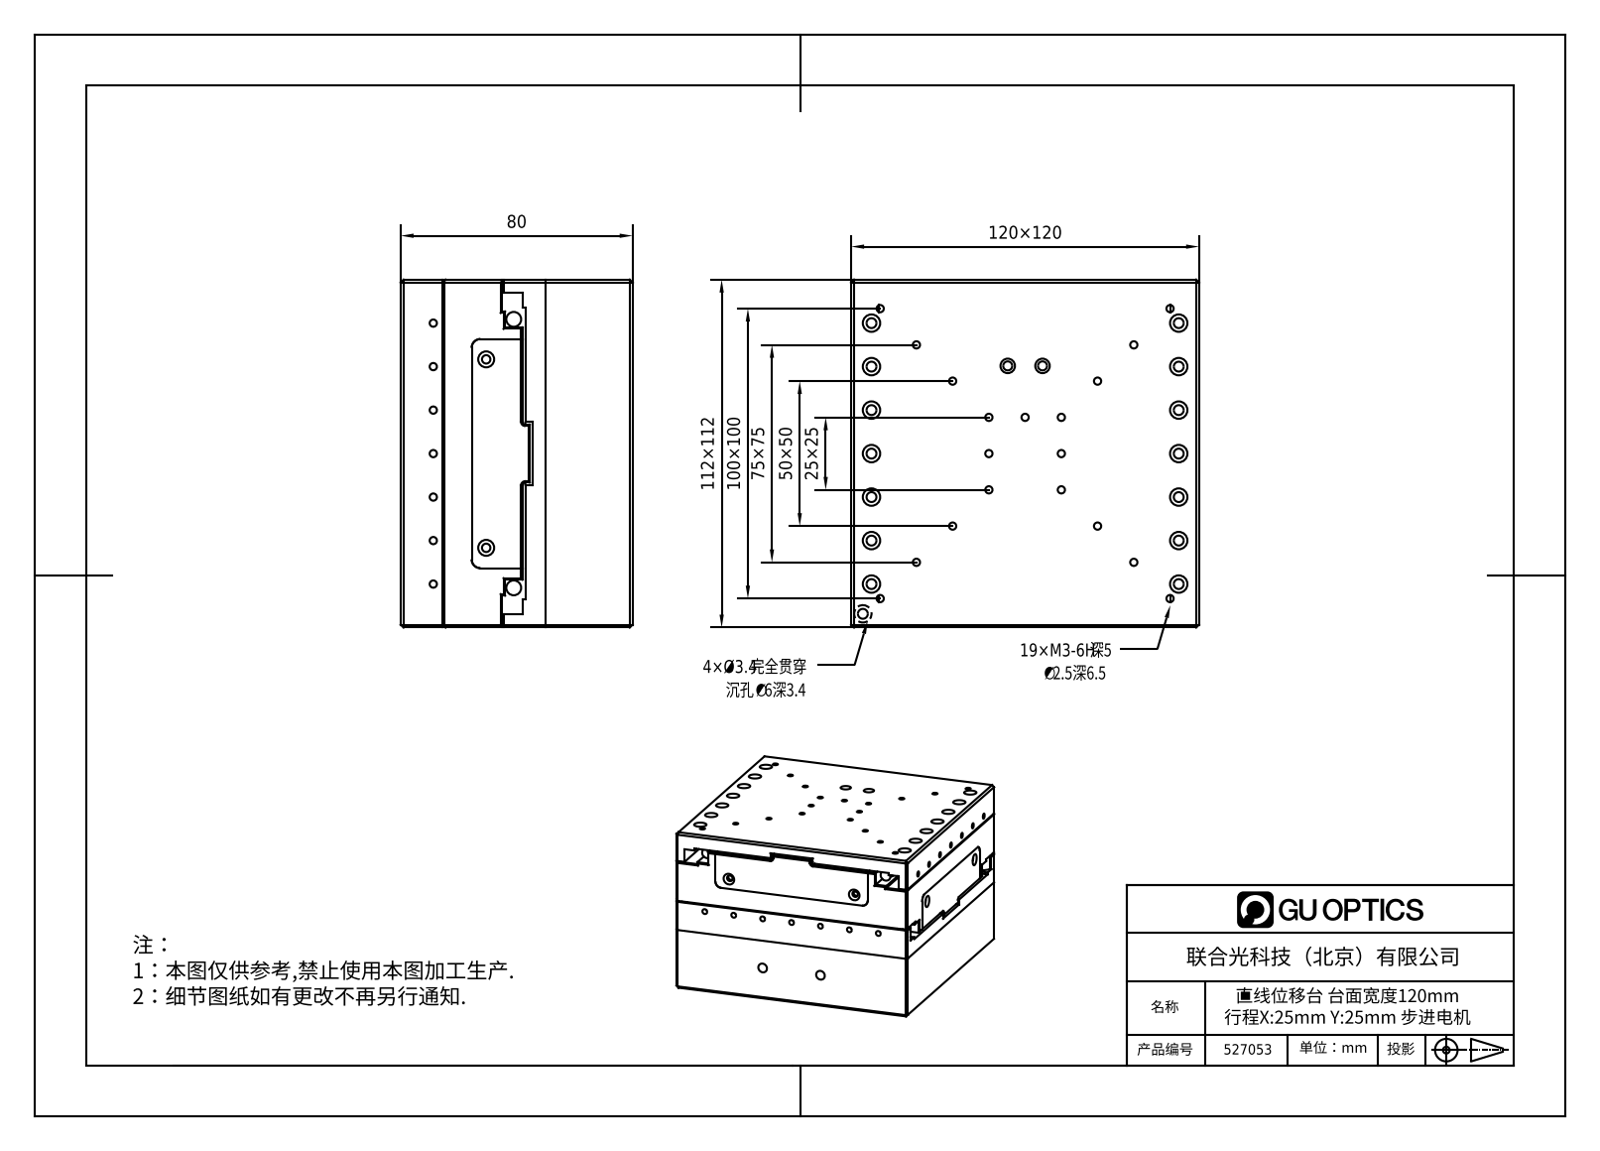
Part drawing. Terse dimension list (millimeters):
name: FMSXY120-25
written by: SolidWorks 2017 (AUTOMOTIVE_DESIGN)
unit: mm
bodies: 0 solids, 423 faces (199 planar, 184 cylindrical, 40 other)
size: 120 × 120 × 80
holes: 33× ⌀2.5, 22× ⌀6, 4× ⌀2.9, 4× ⌀4, 4× ⌀6.5, 3× ⌀3.7, 2× ⌀4.5, 2× ⌀5
rounds: 4× R1, 4× R3
face distances: 7, 120, 36, 43, 0.5, 1, 35, 36.5, 72.5, 79.5
hole spacings: 15, 30, 88.39, 17.68, 27.95, 45.07, 62.5, 45
